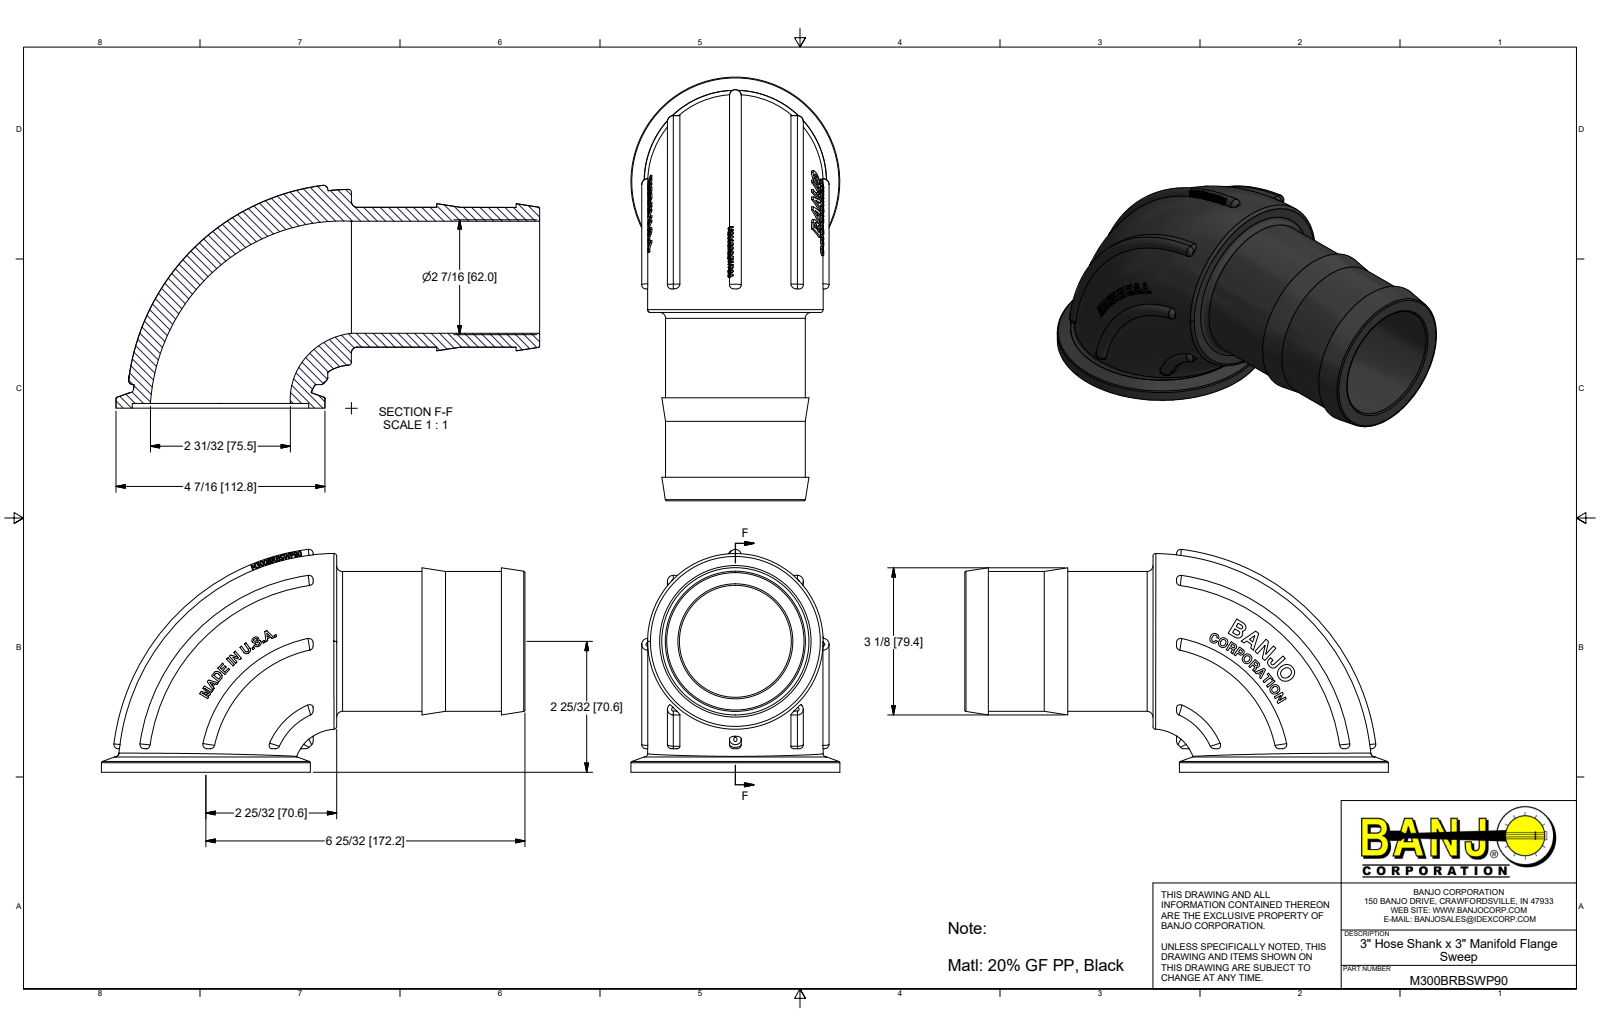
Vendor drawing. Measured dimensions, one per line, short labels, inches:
name: M300BRBSWP90
written by: Autodesk Inventor 2018 (AUTOMOTIVE_DESIGN)
unit: in
bodies: 1 solid, 661 faces (294 planar, 17 cylindrical, 350 other)
size: 9 × 4.733 × 4.44
volume: 34.75 in³; area: 180.1 in²
holes: 1× ⌀2.38, 1× ⌀3.75
bosses: 1× ⌀4.44, 1× ⌀2.969
rounds: 4× R0.09, 1× R1.336, 1× R4.224
face distances: 0.1, 4, 0.5, 2.187, 1.687, 3.5, 1.813, 0.324, 0.224, 0.041
